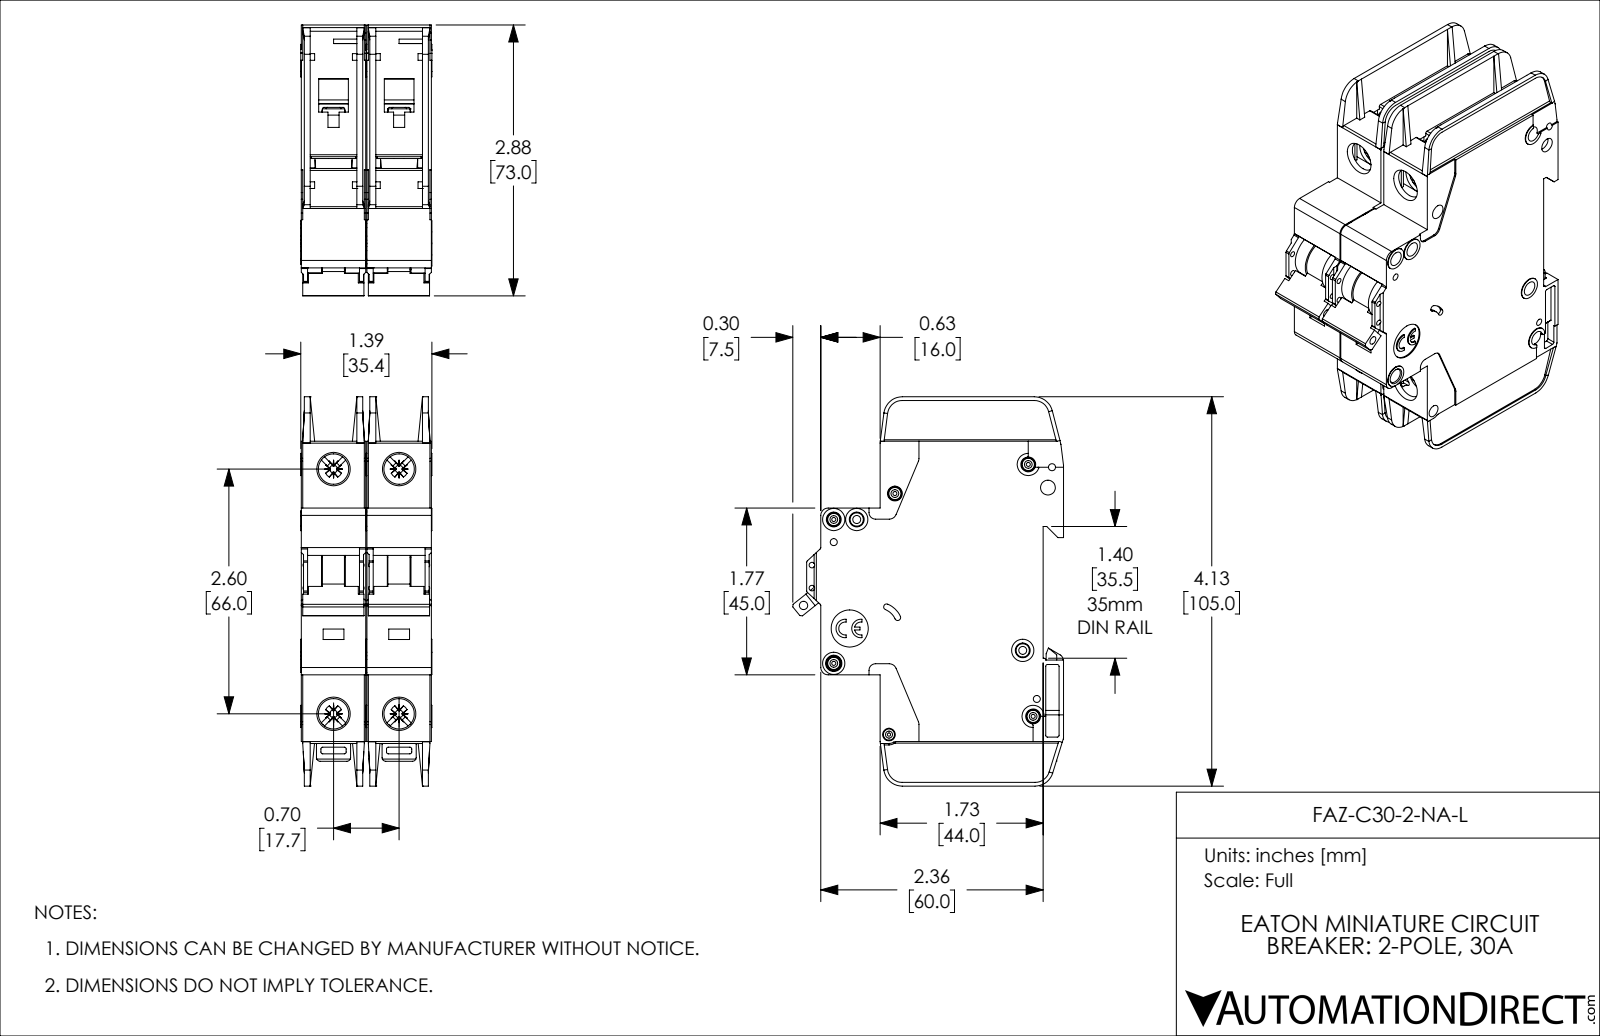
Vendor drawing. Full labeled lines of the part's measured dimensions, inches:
Part name (STEP PRODUCT): FAZ-C30-2-NA-L
STEP written by: SolidWorks 2019 (AUTOMOTIVE_DESIGN)
Units: inches
Bodies: 2 solids, 2254 faces (1342 planar, 714 cylindrical, 198 other)
Overall size (bounding box): 4.134 × 2.876 × 1.394
Volume: 9.365 in³ · Surface area: 82.01 in²
Round holes (diameter × count): ⌀0.157 ×8, ⌀0.043 ×5, ⌀0.075 ×4, ⌀0.323 ×4, ⌀0.059 ×2, ⌀0.085 ×2, ⌀0.035 ×1, ⌀0.089 ×1, ⌀0.098 ×1, ⌀0.134 ×1, ⌀0.394 ×1
Round bosses / shafts (diameter × count): ⌀0.13 ×5, ⌀0.236 ×4, ⌀0.118 ×3, ⌀0.098 ×2
Partial cylindrical surfaces — rounded edges, fillets, slot ends (radius × count): R0.02 ×57, R0.016 ×20, R0.039 ×14, R0.079 ×10, R0.043 ×8, R0.008 ×5, R0.197 ×5, R0.01 ×4
Main face-to-face distances: 0.697, 0.047, 0.685, 0.591, 0.094, 0.638, 0.543, 1.382, 0.744, 0.65
Hole centre spacings: 0.244, 0.537, 0.697, 0.87, 2.598, 2.69, 0.189, 0.199
